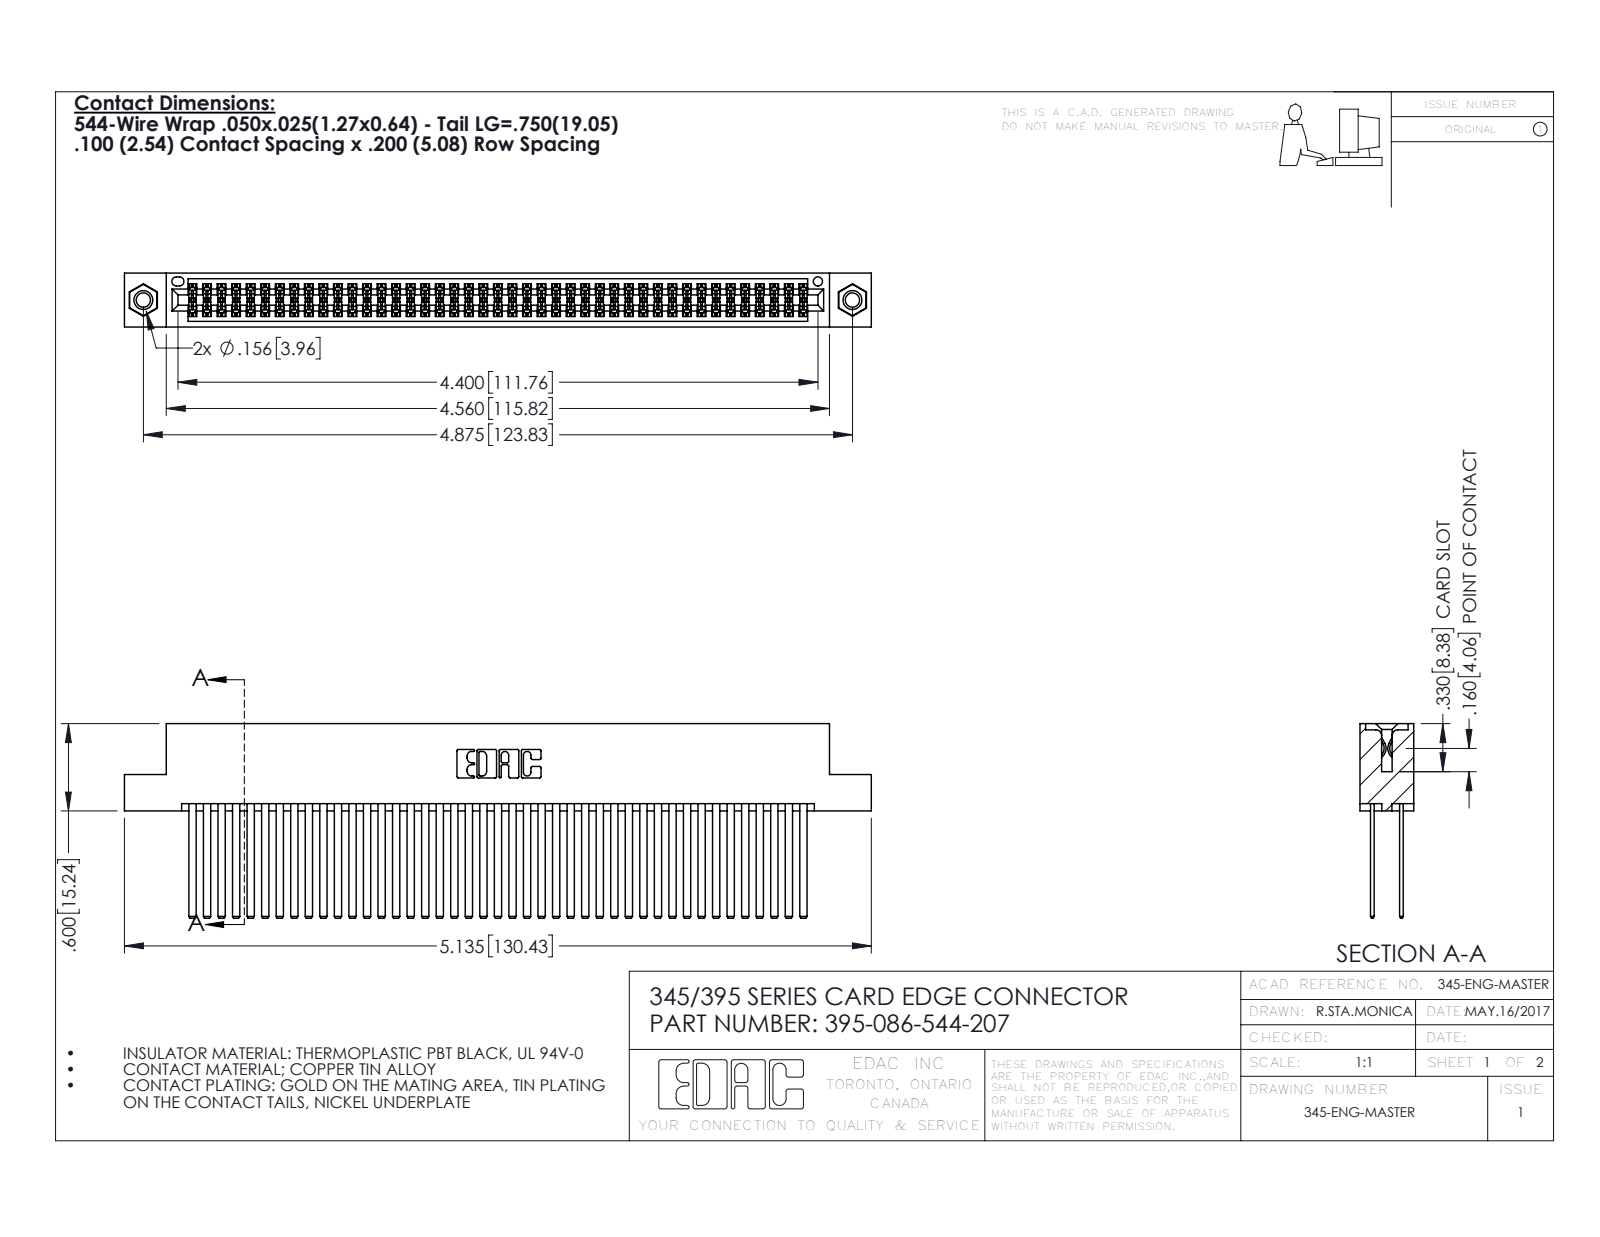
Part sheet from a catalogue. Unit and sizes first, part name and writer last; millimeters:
Units: millimetres
Overall size (bounding box): 130.4 × 34 × 9.4
Round holes (diameter × count): ⌀2.5 ×2, ⌀3.2 ×2, ⌀4 ×2, ⌀1.6 ×1
Round bosses / shafts (diameter × count): ⌀3.9 ×2
Partial cylindrical surfaces — rounded edges, fillets, slot ends (radius × count): R0.2 ×129, R0.3 ×22, R0.2 ×6, R0.8 ×6, R0.7 ×3, R0.4 ×2, R0.5 ×2, R0.6 ×2
Main face-to-face distances: 5.1, 0.6, 1.8, 2.5, 6.9, 7.6, 5.7, 4.4, 9.4, 1.3
Hole centre spacings: 6.9, 117.8, 123.8
Volume: 13 900 mm³ · Surface area: 24 080 mm²
Bodies: 89 solids, 3970 faces (2606 planar, 1348 cylindrical, 16 other)
Part name (STEP PRODUCT): 345 Part_Flush Mounting Lugs - 0.156 Dia-TI; 395-086-544-207; 345-292-001_345-293-144; 345-250-001_345-250-005-103
STEP written by: SolidWorks 2016 (CONFIG_CONTROL_DESIGN)
